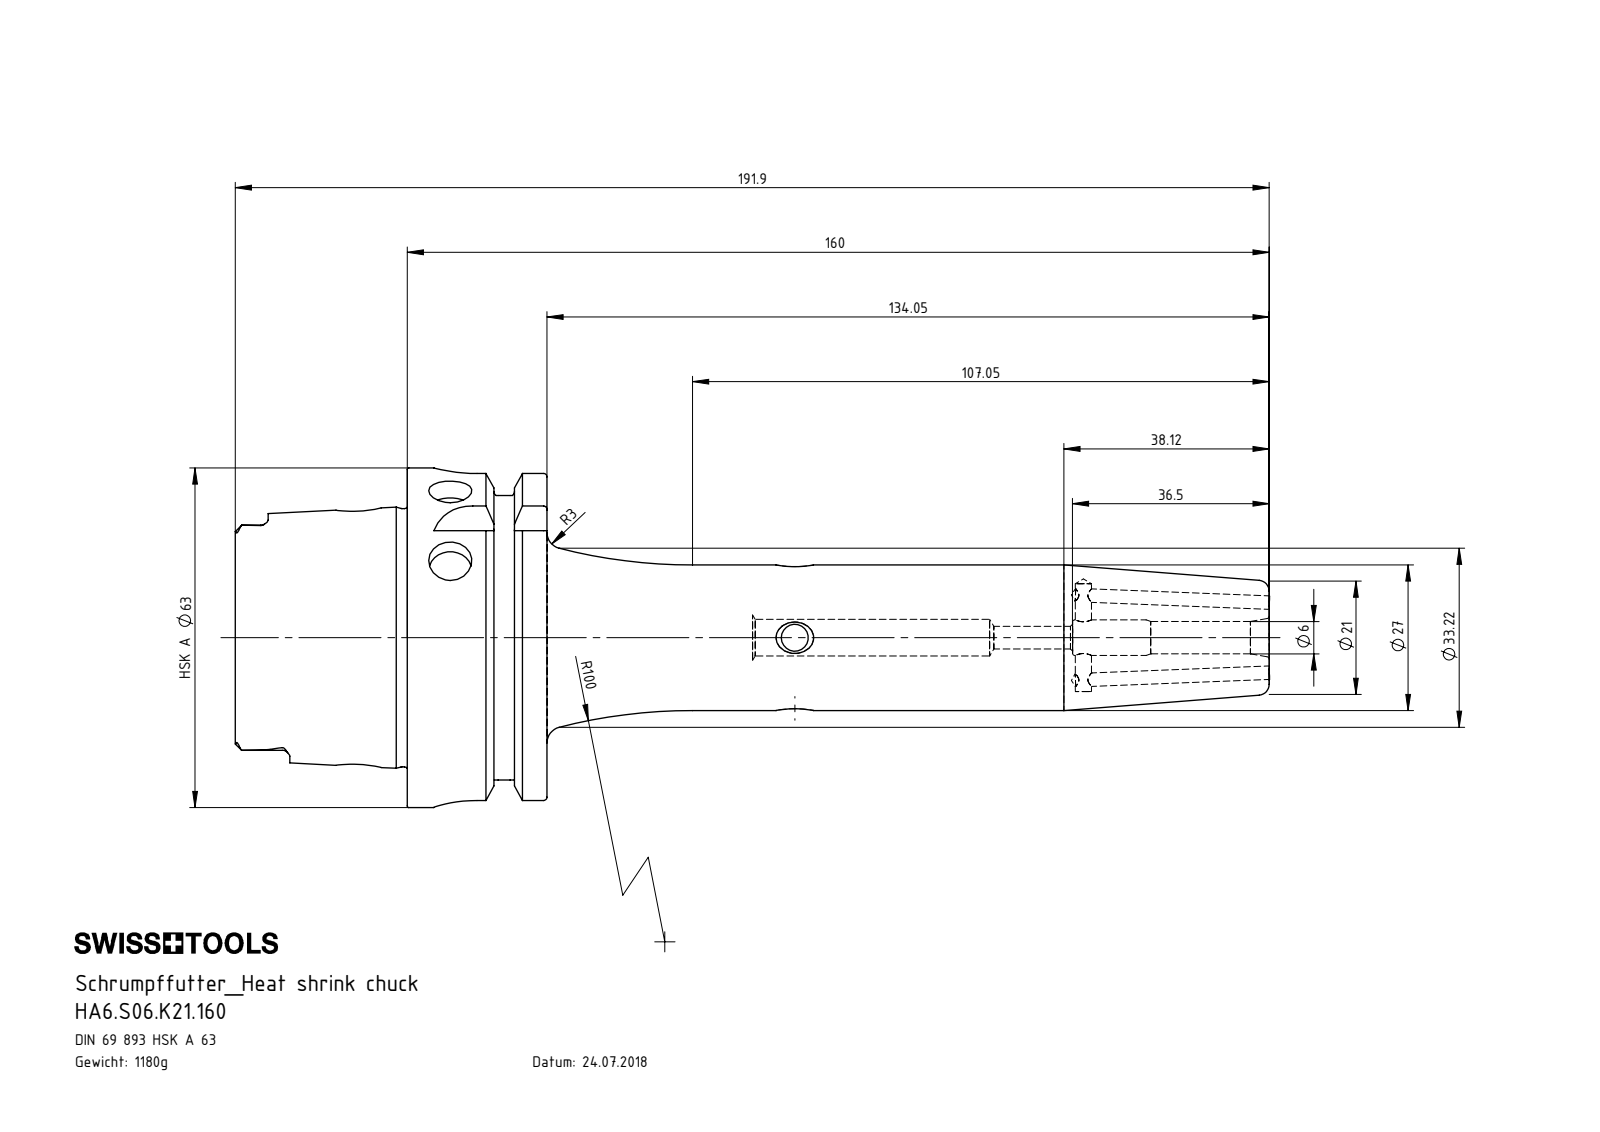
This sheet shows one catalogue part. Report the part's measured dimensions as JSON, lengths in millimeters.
{"part_name": "HA6-S06.K21.160; ERU-AN1.K01.014_A; HA6-S06.K21.160_C_Fertigbearbeitung", "step_written_by": "SolidWorks 2012 (CONFIG_CONTROL_DESIGN)", "units": "millimeters", "bodies": {"solids": 2, "faces": 273, "planar": 83, "cylindrical": 83, "other": 107}, "overall_size": [191.9, 63, 63], "volume_mm3": 150244, "surface_area_mm2": 37368, "round_holes": [[2.5, 3], [5, 2], [8, 2], [3, 1], [4.2, 1], [6, 1], [6.6, 1], [6.8, 1], [7.5, 1], [8.4, 1], [10, 1], [17, 1]], "round_bosses_or_shafts": [[63, 1], [54.95, 1], [47.93, 1], [27, 1], [5, 1]], "partial_cylinders_radius": [[1.4, 6], [2.88, 4], [8, 4]], "face_to_face_distances": [25.95, 16, 9.95, 31.9, 41.85, 57.85, 52.8, 21.8, 11.85, 53.7], "hole_center_spacings": [53.55, 64.95, 80.95, 134.5]}
